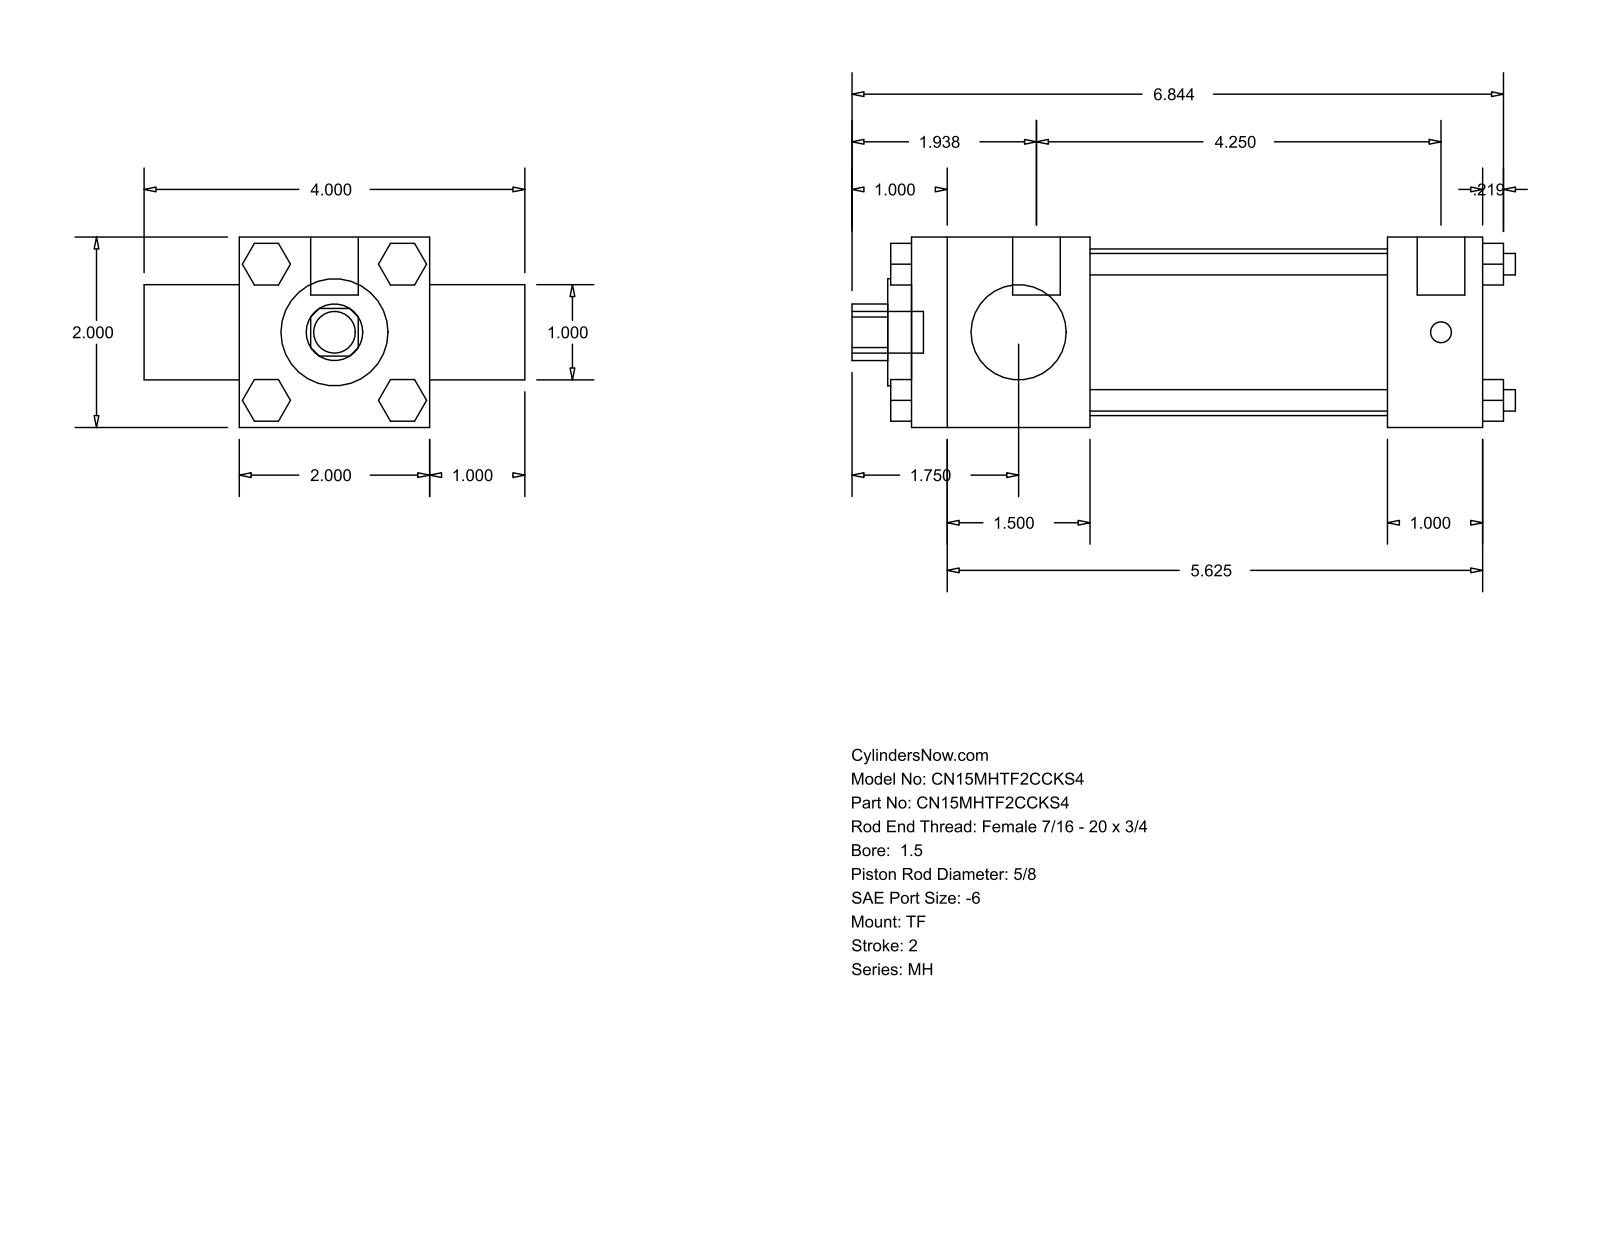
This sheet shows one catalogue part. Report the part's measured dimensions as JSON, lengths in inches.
{"part_name": "MH_TF__0150_0.625", "step_written_by": "GSSL Pune (CONFIG_CONTROL_DESIGN)", "units": "inches", "bodies": {"solids": 0, "faces": 120, "planar": 92, "cylindrical": 28, "other": 0}, "overall_size": [6.969, 4, 2], "round_holes": [[0.625, 1], [1, 1], [1.125, 1], [1.75, 1]], "round_bosses_or_shafts": [[0.225, 4], [0.219, 3], [0.5, 2], [0.437, 1]], "partial_cylinders_radius": [[0.297, 1]], "face_to_face_distances": [2, 1, 6, 3, 1.875, 4.125, 5, 3.125, 0.437, 0.715]}
